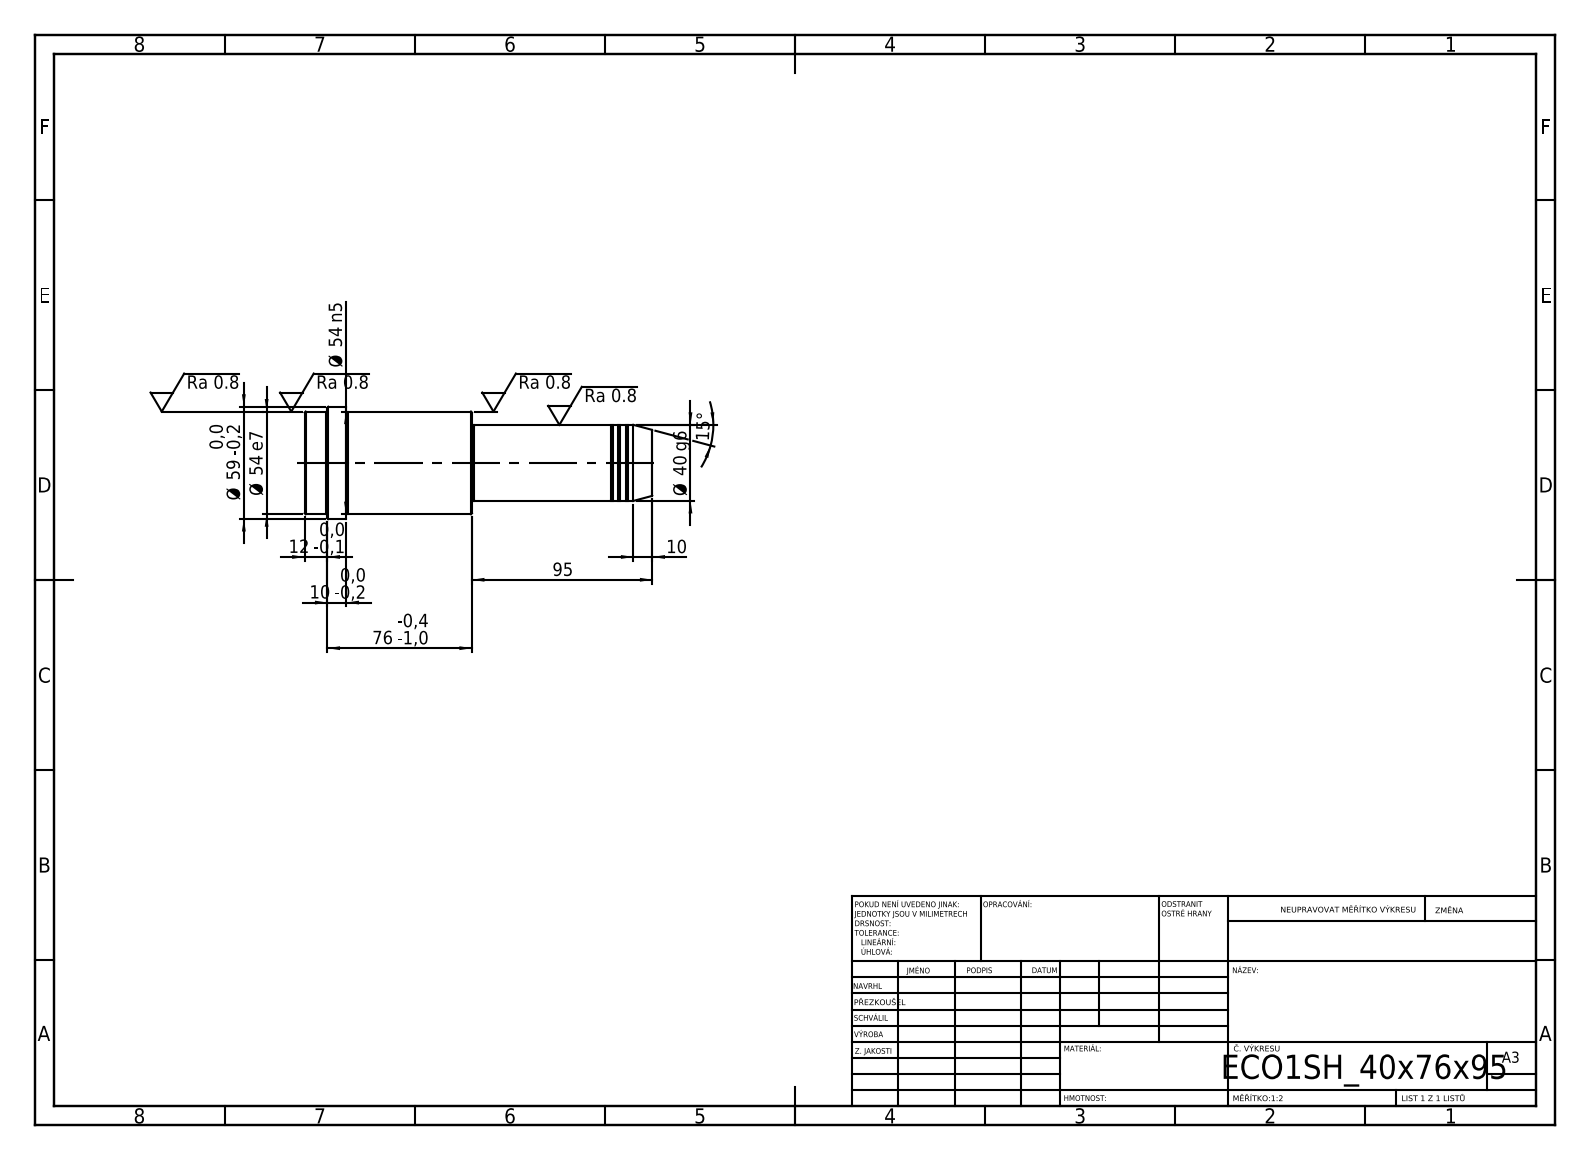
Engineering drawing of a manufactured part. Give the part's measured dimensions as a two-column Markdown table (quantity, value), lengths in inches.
| quantity | value |
| --- | --- |
| STEP written by | SolidWorks 2019 (CONFIG_CONTROL_DESIGN) |
| units | inches |
| bodies | 1 solid, 52 faces (6 planar, 16 cylindrical, 30 other) |
| overall size | 7.205 × 2.323 × 2.323 |
| volume | 19.73 in³ |
| surface area | 50.35 in² |
| round bosses / shafts (diameter × count) | 2.323 × 1, 2.126 × 1, 1.575 × 1, 1.535 × 1 |
| main face-to-face distances | 3.465, 3.74, 7.205, 6.339, 2.598, 0.866, 6.732, 2.992, 0.394, 0.472 |
